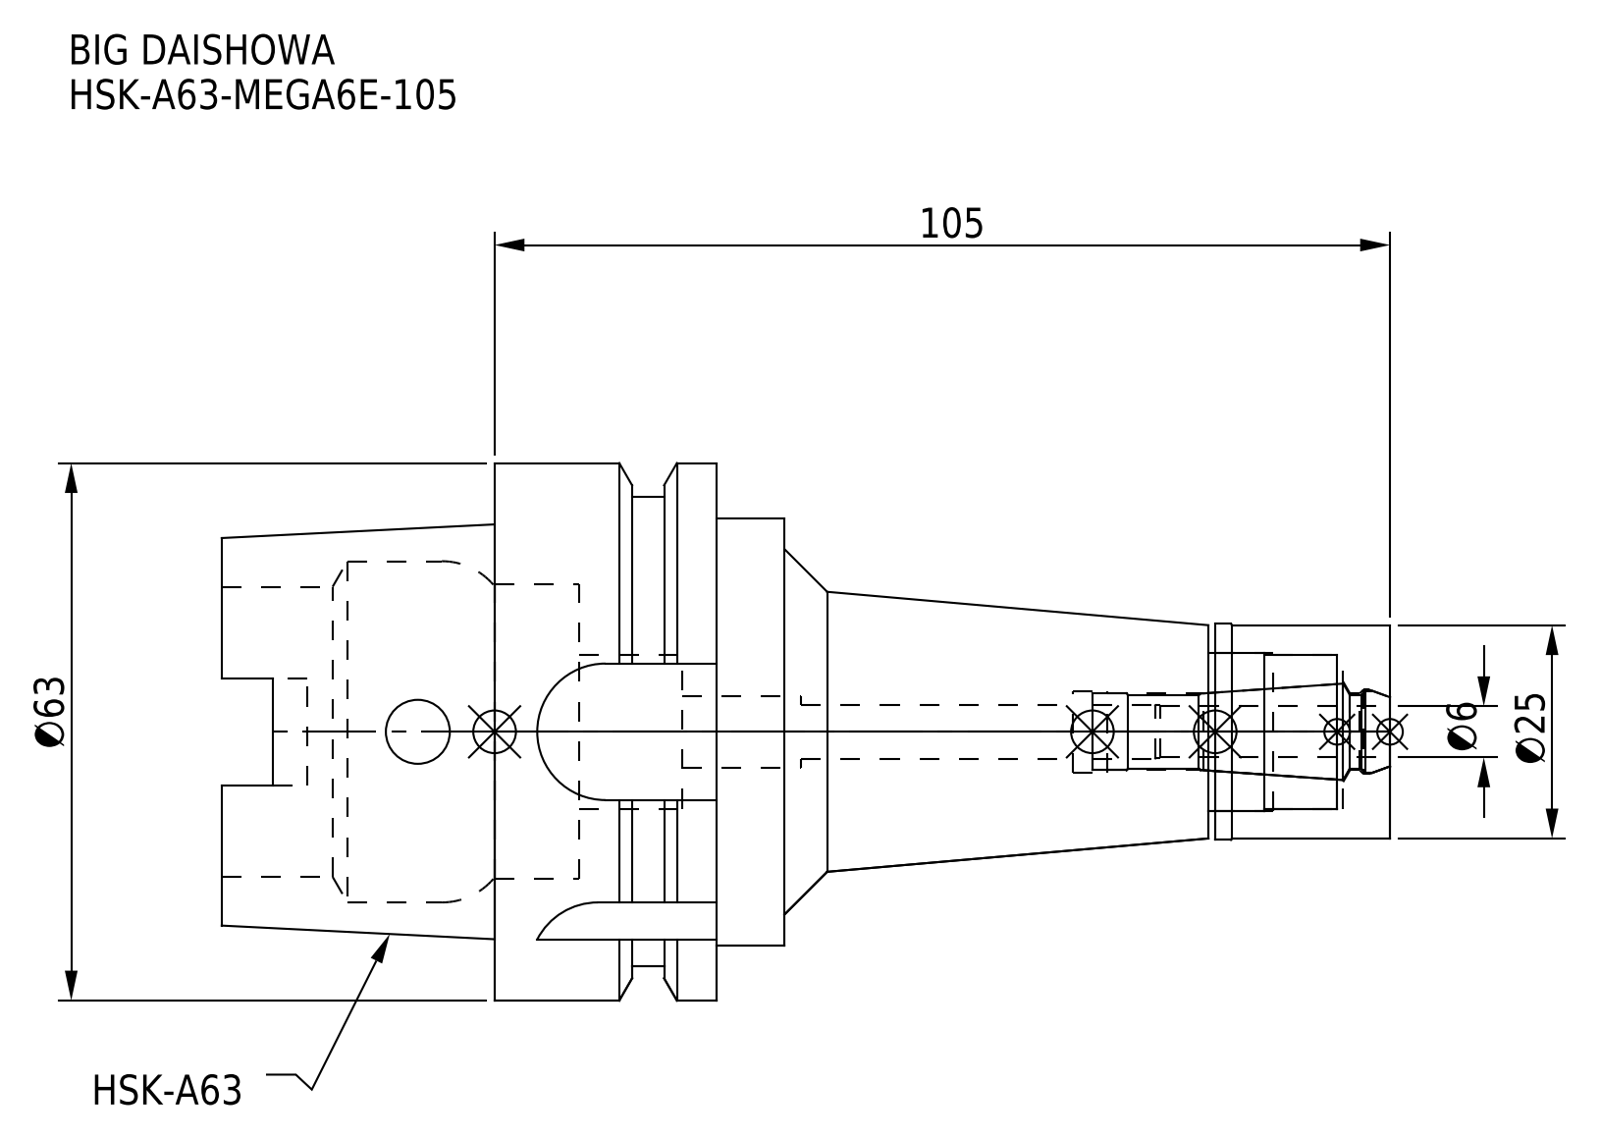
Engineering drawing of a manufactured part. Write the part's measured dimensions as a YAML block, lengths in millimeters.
part_name: "MEN6_1.stp; HSK-A63-MEGA6E-105-060-FreeParts; DXF_TEMP_ASSY_ASM_4_ASM.stp; HA63ME06105-060_ASM.stp (+3 more)"
step_written_by: "SolidWorks 2019 (CONFIG_CONTROL_DESIGN)"
units: millimeters
bodies: {solids: 2, faces: 127, planar: 45, cylindrical: 54, other: 28}
overall_size: [137, 63, 63]
volume: 138420
surface_area: 33781
round_holes:
  - {diameter: 6.4, count: 1}
  - {diameter: 7.5, count: 1}
  - {diameter: 8.4, count: 1}
  - {diameter: 9, count: 1}
  - {diameter: 9.6, count: 1}
  - {diameter: 9.9, count: 1}
  - {diameter: 18, count: 1}
  - {diameter: 18.5, count: 1}
  - {diameter: 34, count: 1}
  - {diameter: 34.5, count: 1}
  - {diameter: 40, count: 1}
round_bosses_or_shafts:
  - {diameter: 63, count: 1}
  - {diameter: 55, count: 1}
  - {diameter: 50, count: 1}
  - {diameter: 25.3, count: 1}
  - {diameter: 25, count: 1}
partial_cylinders:
  - {radius: 2.8, count: 2}
  - {radius: 2.88, count: 2}
  - {radius: 8, count: 2}
  - {radius: 9, count: 1}
face_to_face_distances: [26, 9.95, 16.05, 8, 24.05, 34, 71, 79, 95.05, 105]
